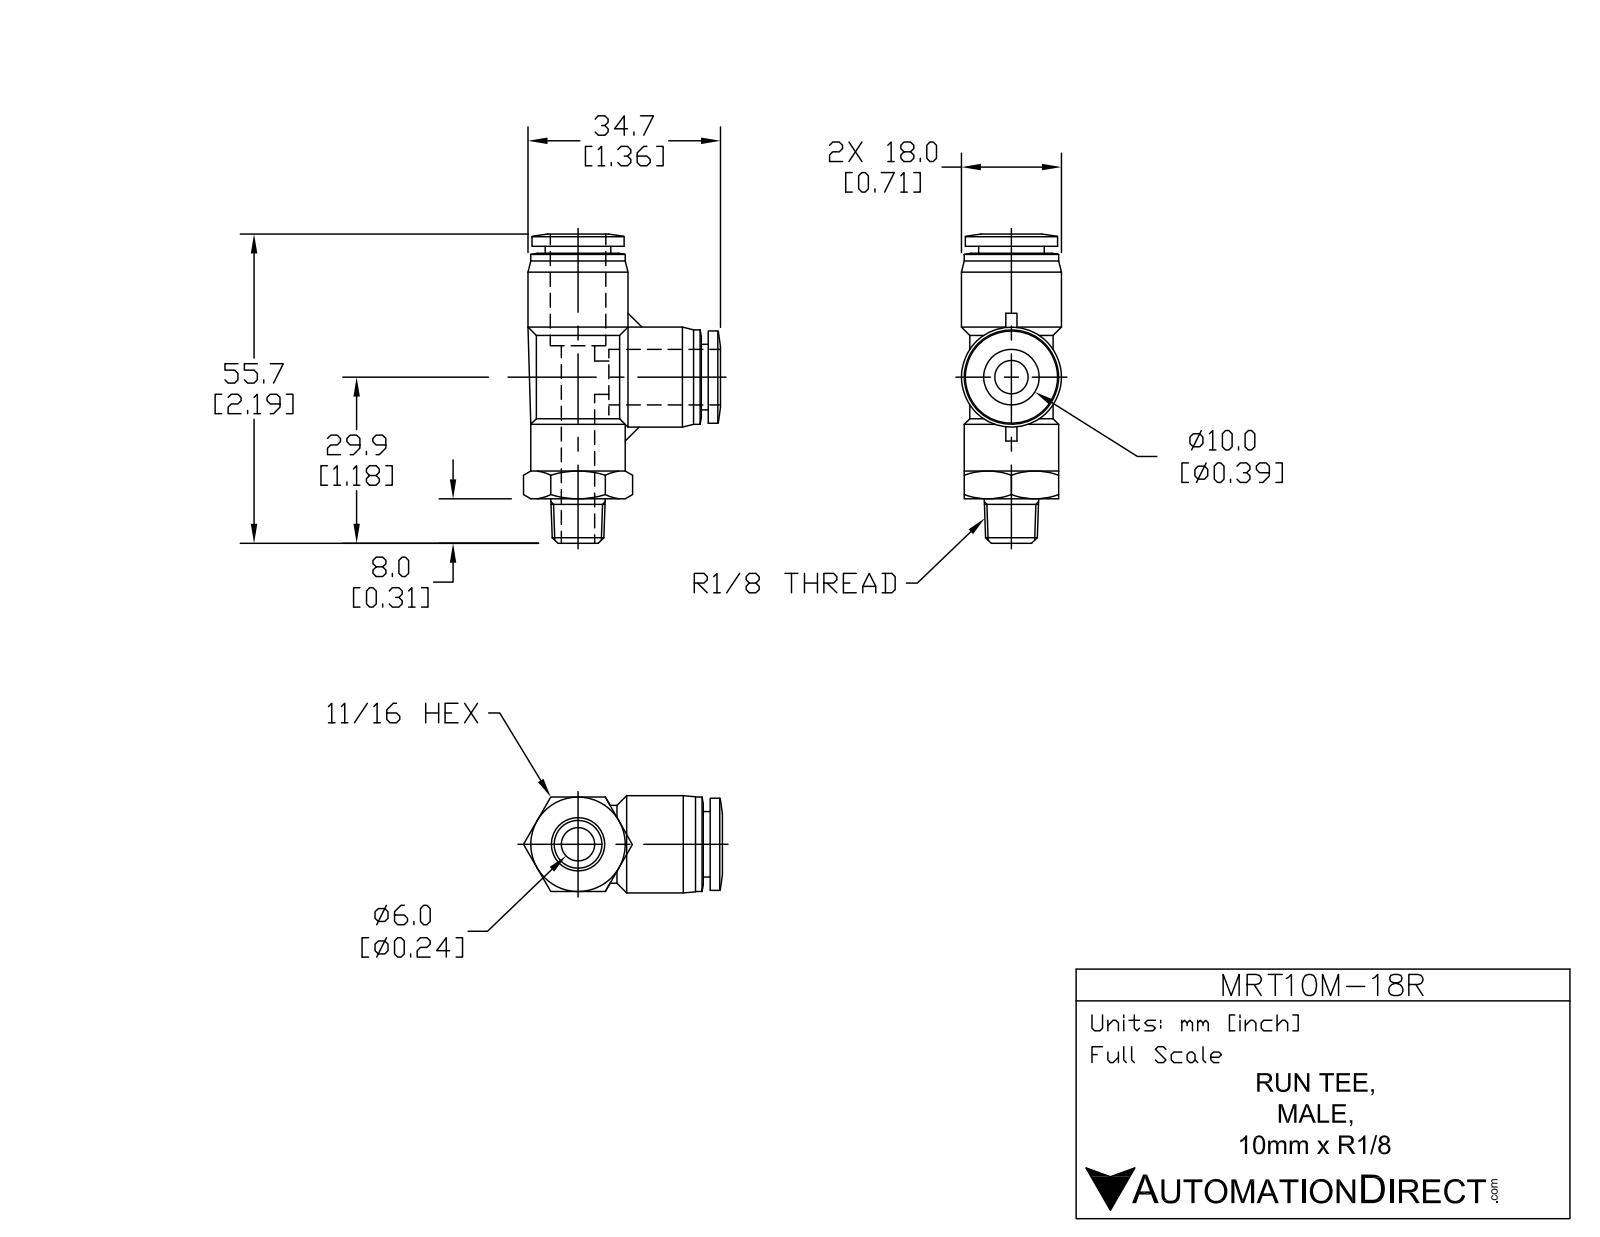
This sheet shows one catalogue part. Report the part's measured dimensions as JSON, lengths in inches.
{"part_name": "MRT10M-18R", "step_written_by": "SolidWorks 2015 (AUTOMOTIVE_DESIGN)", "units": "inches", "bodies": {"solids": 1, "faces": 103, "planar": 24, "cylindrical": 32, "other": 47}, "overall_size": [2.195, 1.4, 0.709], "volume_in3": 0.661, "surface_area_in2": 10.39, "round_holes": [[0.236, 2], [0.406, 2]], "round_bosses_or_shafts": [[0.709, 2], [0.669, 2], [0.654, 2], [0.591, 2], [0.465, 2]], "face_to_face_distances": [0.669, 0.049, 0.659, 0.709, 1.793, 1.744, 0.295, 0.374, 1.085, 0.079]}
